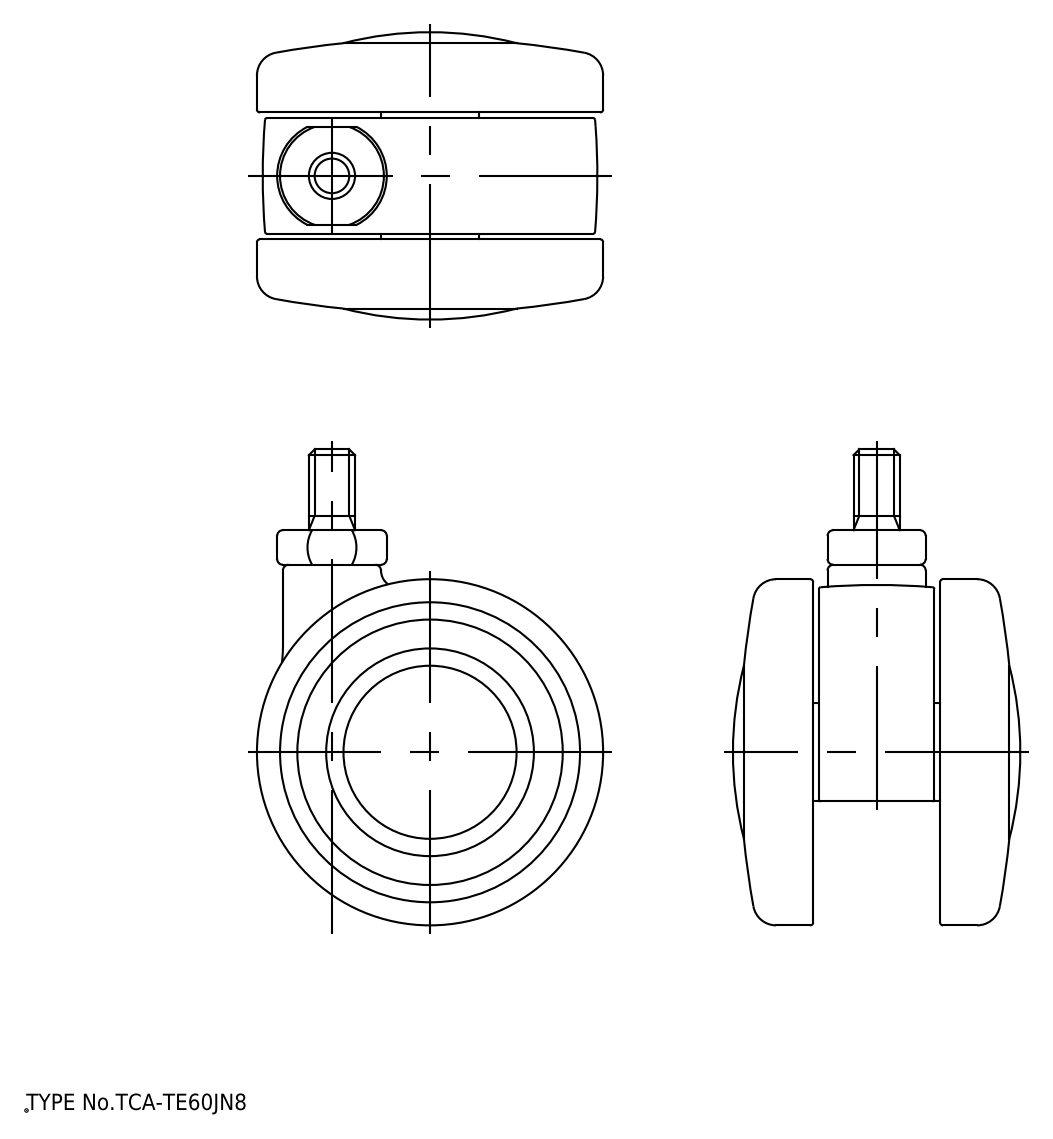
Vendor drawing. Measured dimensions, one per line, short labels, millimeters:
name: TCA-TE60J_Body; TCA-TE60J_Wheel; TCA-TE60JN8_Shaft
written by: spGate 18.9.1 (****-****-****-****) (AUTOMOTIVE_DESIGN)
unit: mm
bodies: 4 solids, 189 faces (46 planar, 75 cylindrical, 68 other)
size: 82.5 × 60 × 49.14
volume: 85 534 mm³; area: 31 705 mm²
holes: 1× ⌀8, 1× ⌀9.3, 1× ⌀10.7, 1× ⌀20, 1× ⌀30.2, 1× ⌀45
bosses: 1× ⌀60, 1× ⌀36, 1× ⌀29.9, 1× ⌀18, 1× ⌀17, 1× ⌀10.5, 1× ⌀8, 1× ⌀6.5
rounds: 5× R0.3, 3× R1, 3× R2, 1× R10, 1× R10.5, 1× R26.5, 1× R29
face distances: 2, 19, 7, 5, 24, 26, 11, 30.5, 28.5, 0.5
